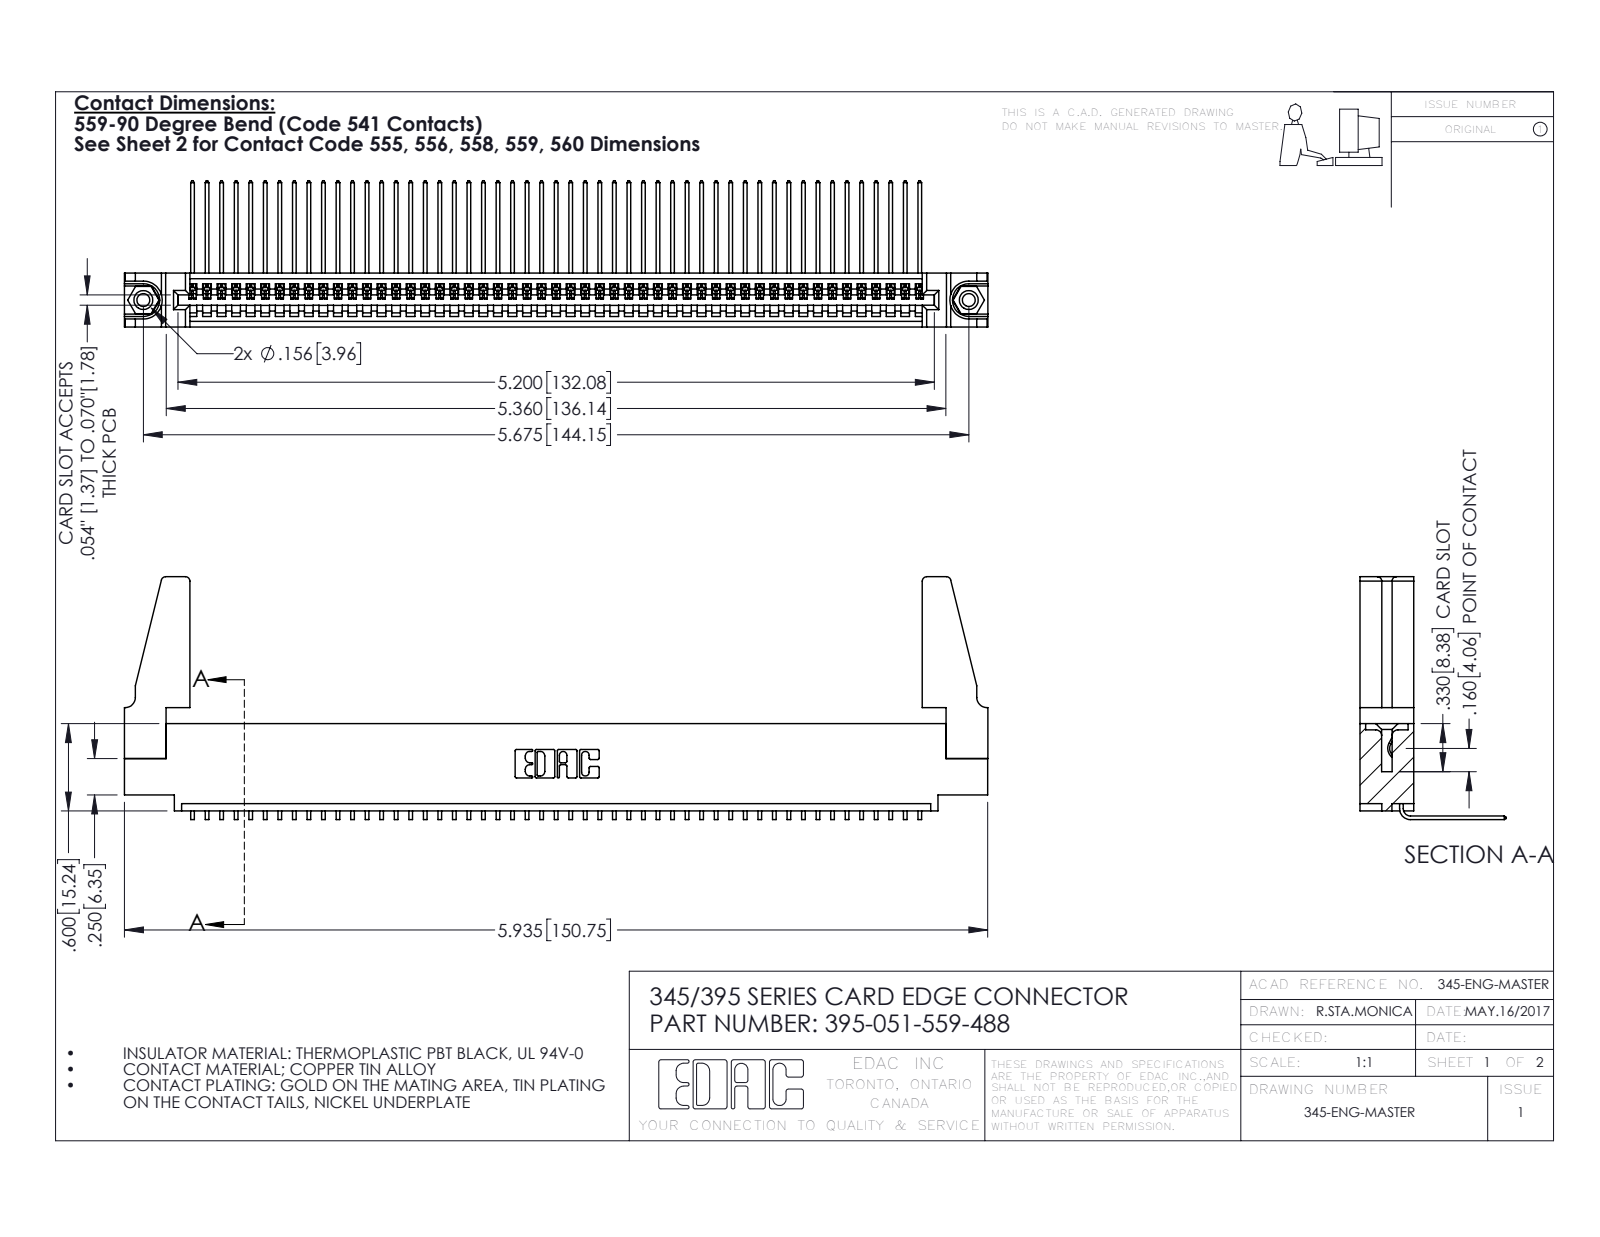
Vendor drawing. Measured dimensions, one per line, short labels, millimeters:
name: 345 Part_0.110 Offset - 0.156 Dia-TH; 345-250-001_345-250-001-102; 395-051-559-488; 345-292-001_558 559 Tail - 1 (+1 more)
written by: SolidWorks 2016 (CONFIG_CONTROL_DESIGN)
unit: mm
bodies: 56 solids, 3314 faces (2298 planar, 1000 cylindrical, 16 other)
size: 150.8 × 42.4 × 25.5
volume: 17 750 mm³; area: 23 590 mm²
holes: 2× ⌀2.3, 2× ⌀3.2, 2× ⌀4, 1× ⌀1.6
bosses: 2× ⌀3.9
rounds: 102× R0.2, 22× R0.3, 8× R0.8, 6× R0.2, 6× R0.8, 3× R0.7, 2× R0.8, 2× R1
face distances: 1.8, 7.6, 9.4, 5.1, 2.5, 6.9, 0.6, 5.7, 3.8, 1.8
hole spacings: 6.9, 138.2, 144.1
